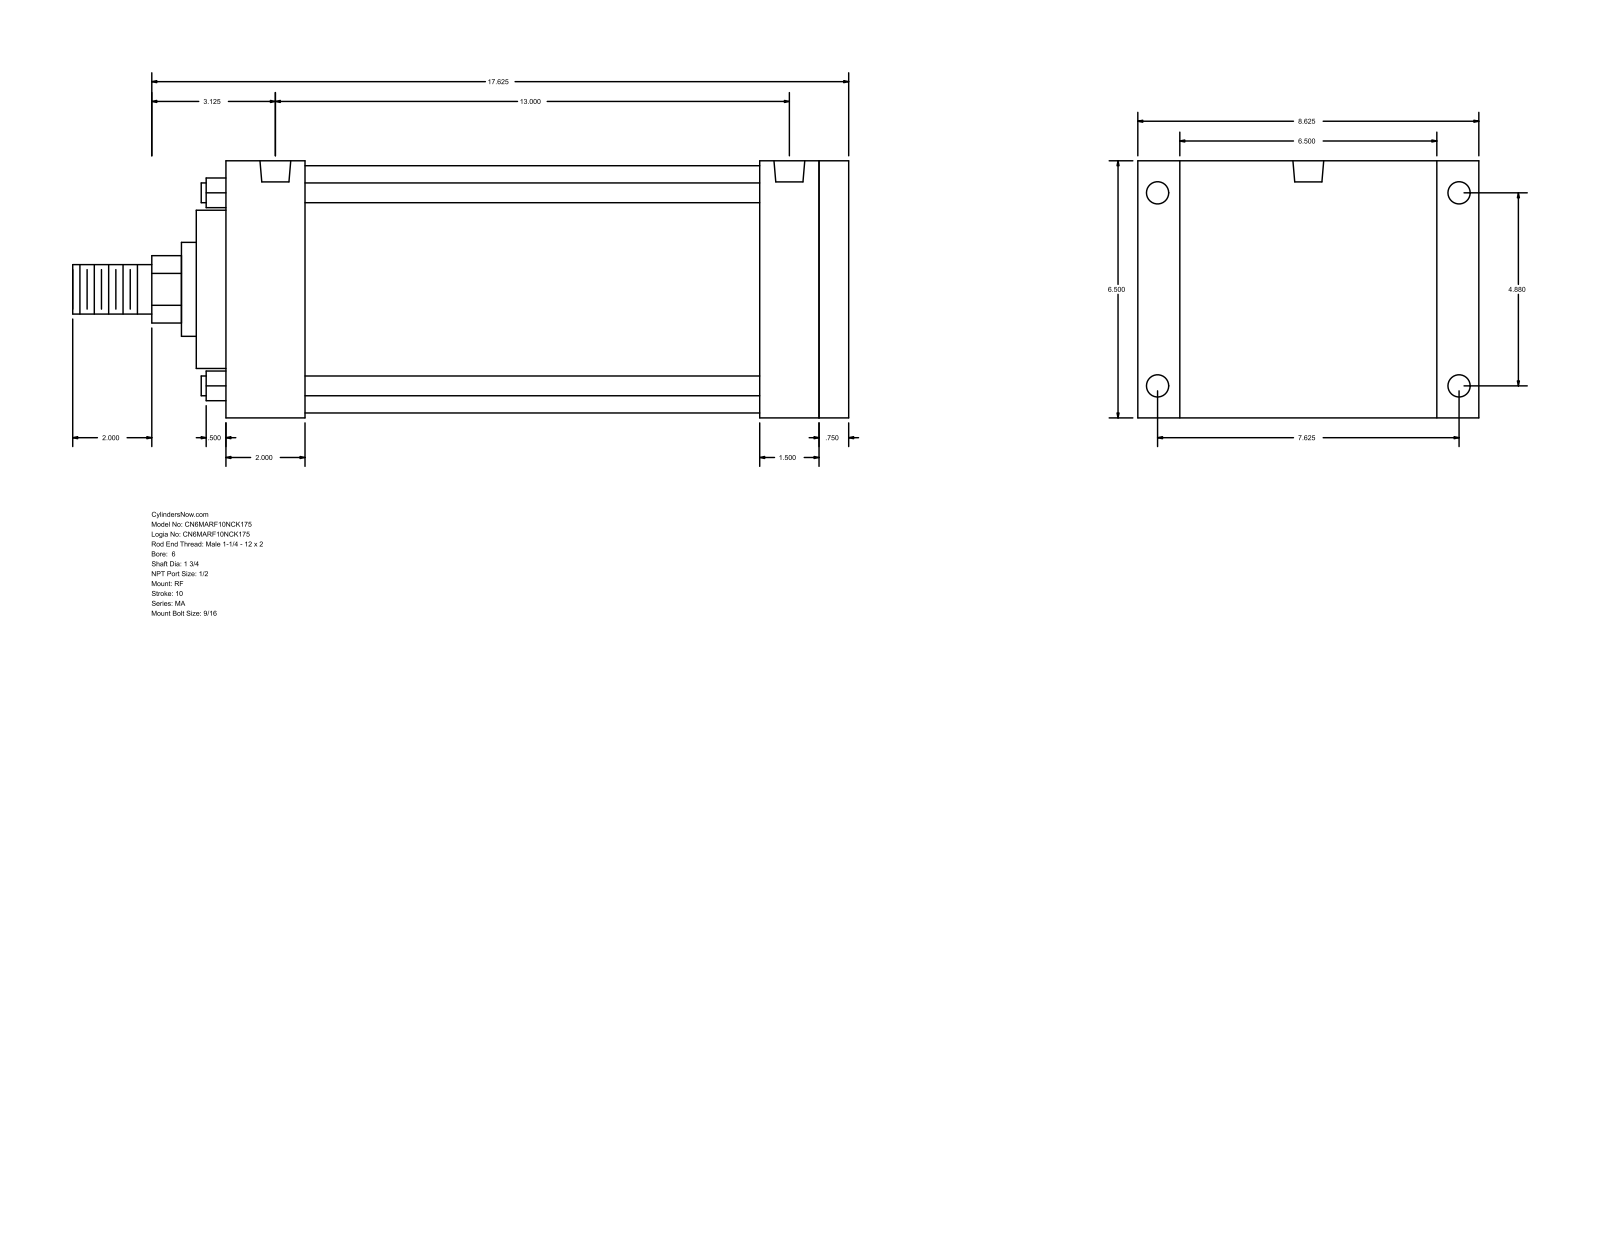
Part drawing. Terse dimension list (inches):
name: MA_RF__0600_1.75
written by: GSSL Pune (CONFIG_CONTROL_DESIGN)
unit: in
bodies: 0 solids, 94 faces (65 planar, 29 cylindrical, 0 other)
size: 19.625 × 8.625 × 6.5
holes: 4× ⌀0.563, 4× ⌀0.687, 2× ⌀0.778
bosses: 4× ⌀0.5, 1× ⌀6.25, 1× ⌀4, 1× ⌀2.375, 1× ⌀1.75, 1× ⌀1.25
rounds: 1× R0.852
face distances: 6.5, 15.75, 15, 0.75, 1.5, 2, 0.75, 13, 13.75, 13.5
hole spacings: 4.88, 7.625, 9.053, 13
